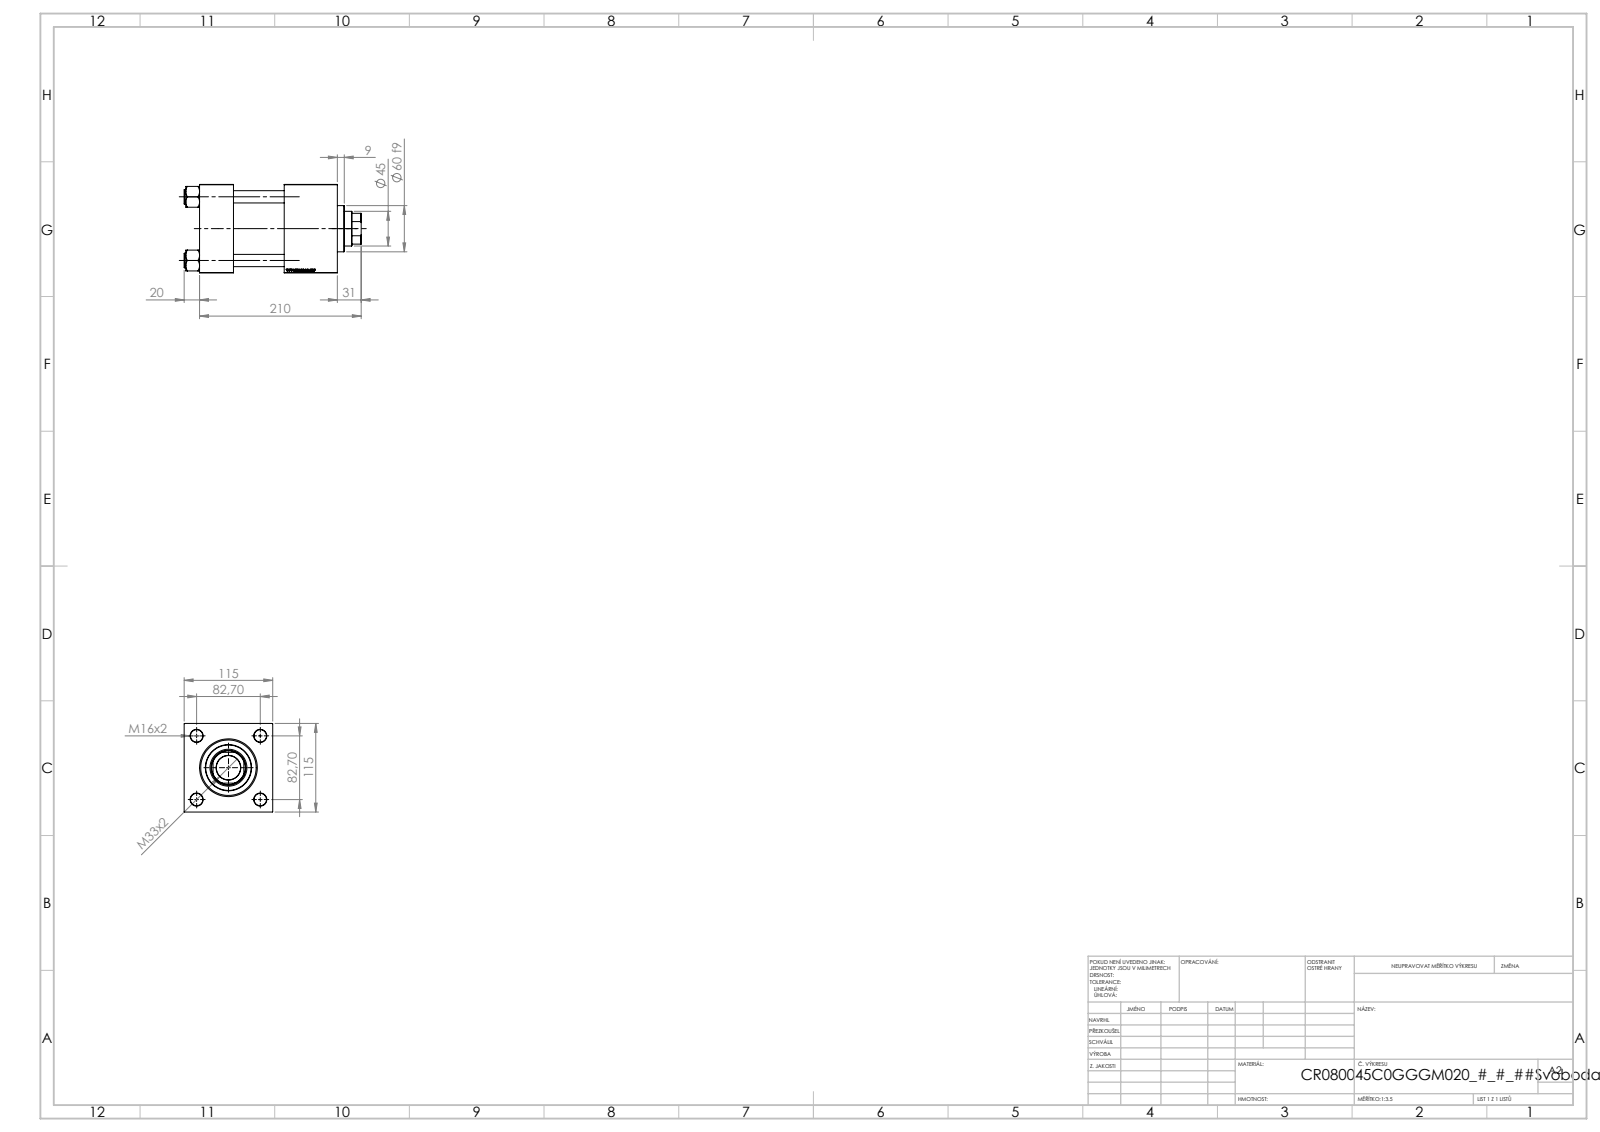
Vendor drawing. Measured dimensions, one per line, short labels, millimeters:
name: V215CR_VCP_C; V215CR_C_Body; V215CR_C_TYCINKA; NUT_M5_C (+1 more)
written by: SolidWorks 2019 (CONFIG_CONTROL_DESIGN)
unit: mm
bodies: 11 solids, 1197 faces (574 planar, 87 cylindrical, 536 other)
size: 230 × 115 × 115
volume: 1 819 000 mm³; area: 273 885 mm²
holes: 4× ⌀16, 2× ⌀7, 2× ⌀26.44, 2× ⌀35, 1× ⌀31.5, 1× ⌀45, 1× ⌀48, 1× ⌀61, 1× ⌀72, 1× ⌀80
bosses: 4× ⌀19, 1× ⌀86, 1× ⌀60
rounds: 1× R22
face distances: 115, 44, 110, 179, 135, 66, 69, 20, 150.3, 106.3
hole spacings: 58.48, 82.7, 116.96, 111
